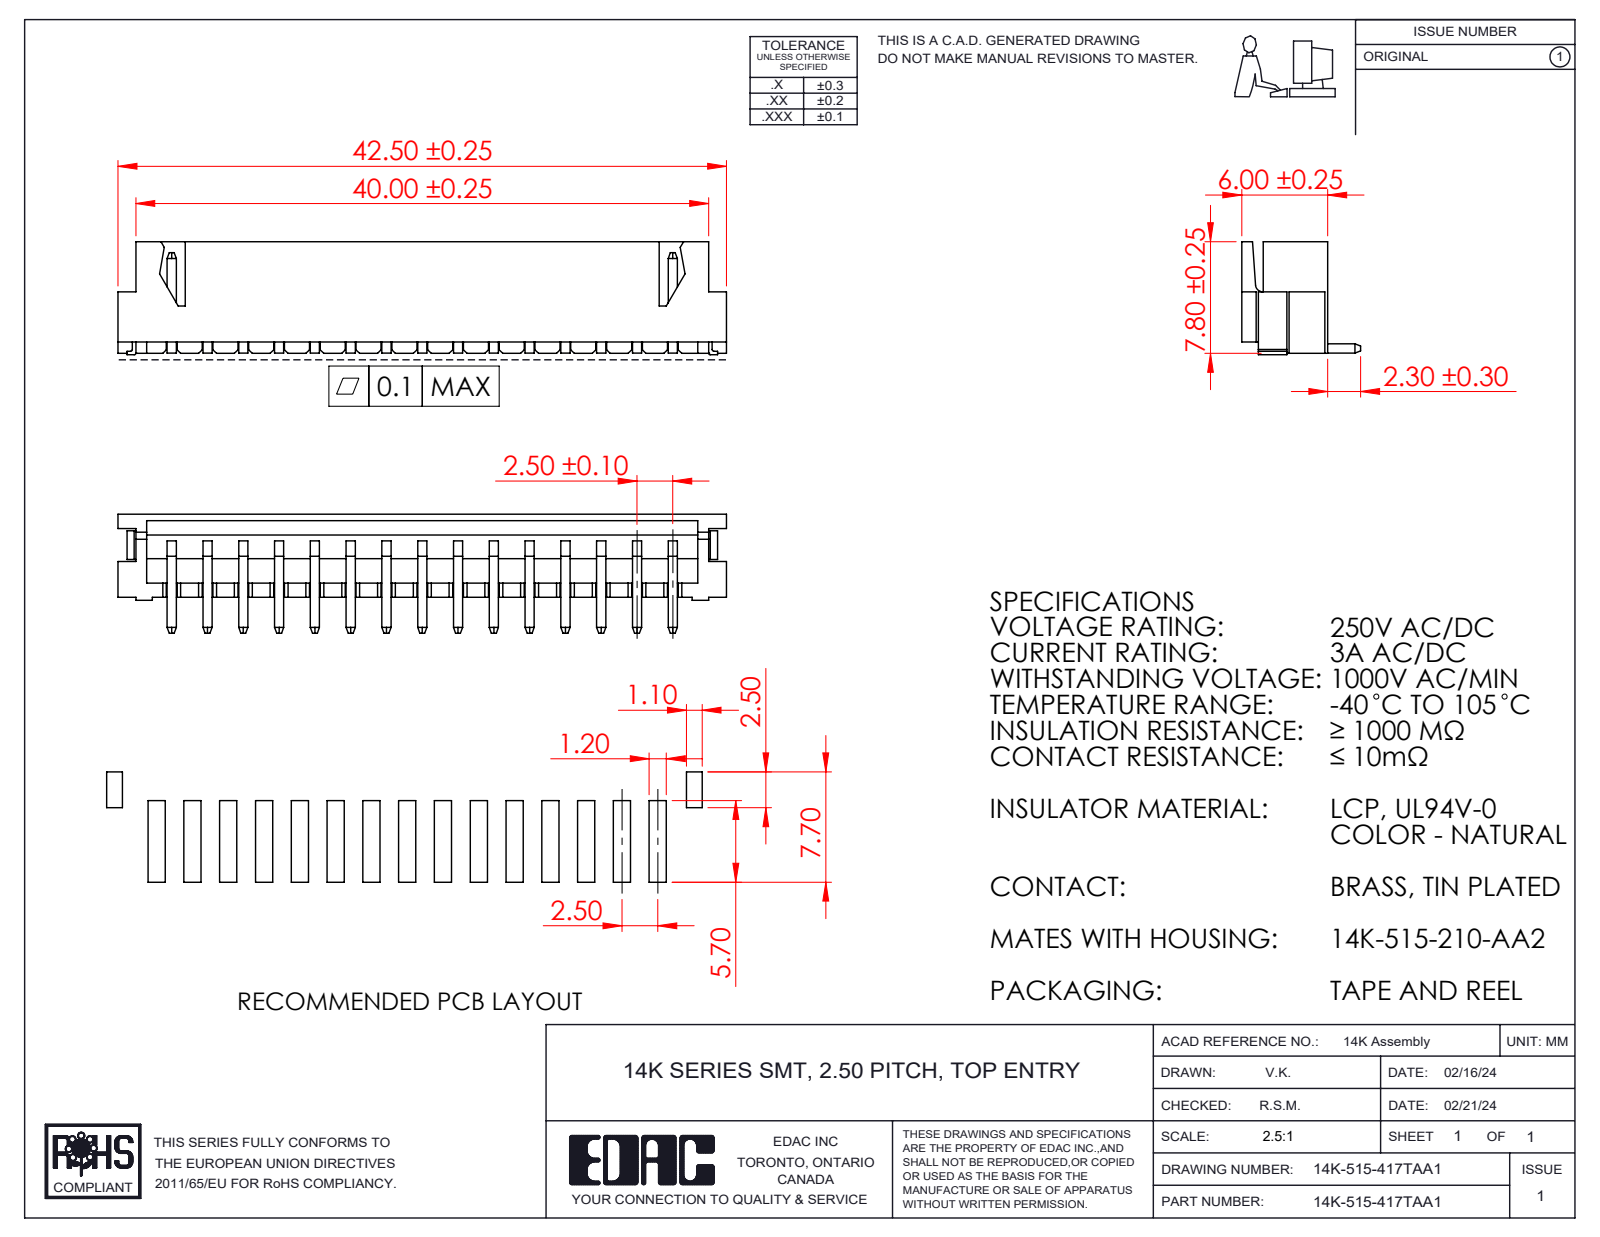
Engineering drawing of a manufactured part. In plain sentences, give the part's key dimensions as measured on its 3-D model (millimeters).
The part is named "14K-515-417TAA1; 14K Series SMT Pin_Top Entry; 14K Series SMT Top Entry Insulator_515". Its 3-D file was written by "SolidWorks 2023 (CONFIG_CONTROL_DESIGN)". It is 16 solids with 742 faces: 676 planar, 66 cylindrical and 0 other. Overall it measures 42.5 by 8.3 by 7.9 millimeters. Its volume is 752 cubic millimeters and its surface area 2 415 square millimeters. Partial cylindrical surfaces (rounded edges, fillets, slot ends): 30 of radius 0.38, 4 of radius 0.12, 1 of radius 0.43, 1 of radius 0.5, 1 of radius 1.07. The main face-to-face distances are 0.75, 5.05, 5.8, 4.3, 2.5, 0.64, 1, 1.75, 2.55, 1.86.
